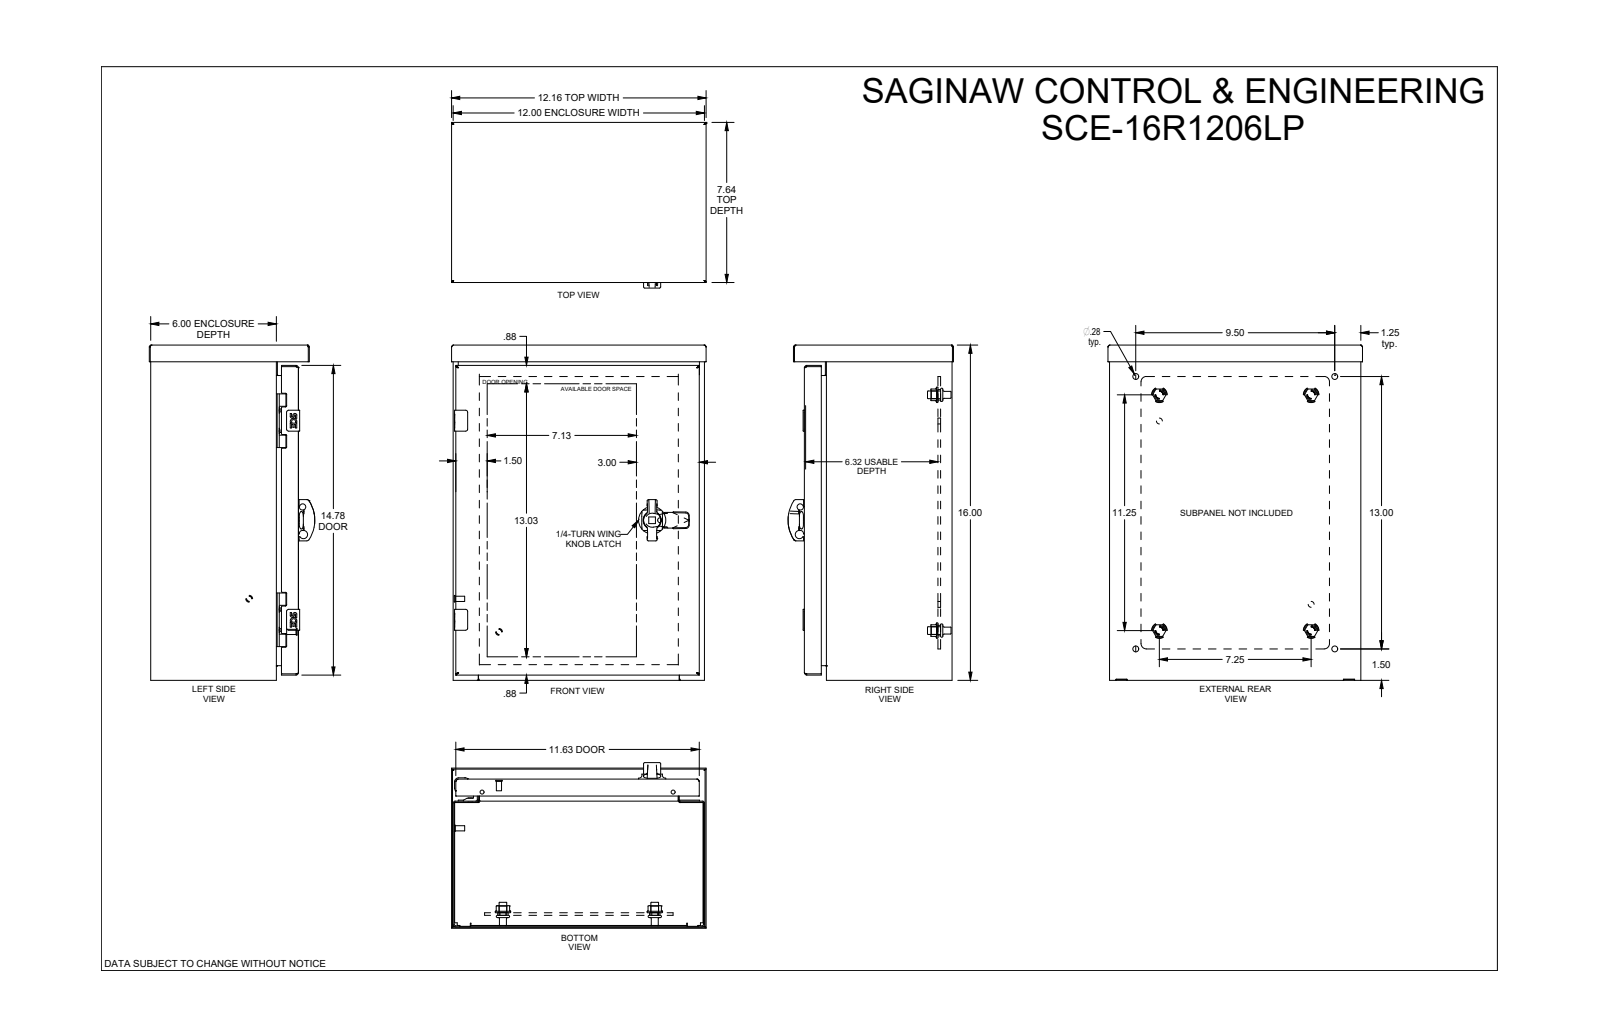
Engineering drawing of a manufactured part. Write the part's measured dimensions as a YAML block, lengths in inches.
part_name: "SCE-16R1206LP_REV2"
step_written_by: "SolidWorks 2021 (AUTOMOTIVE_DESIGN)"
units: inches
bodies: {solids: 25, faces: 1253, planar: 557, cylindrical: 493, other: 203}
overall_size: [16, 12.156, 7.947]
volume: 79.2
surface_area: 2187
round_holes:
  - {diameter: 0.172, count: 4}
  - {diameter: 0.205, count: 4}
  - {diameter: 0.244, count: 4}
  - {diameter: 0.266, count: 4}
  - {diameter: 0.281, count: 4}
  - {diameter: 0.375, count: 4}
  - {diameter: 0.5, count: 4}
  - {diameter: 0.04, count: 2}
  - {diameter: 0.188, count: 2}
  - {diameter: 0.218, count: 2}
  - {diameter: 0.281, count: 2}
  - {diameter: 0.204, count: 1}
round_bosses_or_shafts:
  - {diameter: 0.366, count: 4}
  - {diameter: 0.332, count: 4}
  - {diameter: 0.25, count: 4}
  - {diameter: 0.24, count: 4}
  - {diameter: 0.196, count: 3}
  - {diameter: 0.248, count: 2}
  - {diameter: 1.303, count: 1}
  - {diameter: 0.866, count: 1}
partial_cylinders:
  - {radius: 0.015, count: 36}
  - {radius: 0.06, count: 25}
  - {radius: 0.063, count: 12}
  - {radius: 0.031, count: 10}
  - {radius: 0.062, count: 8}
  - {radius: 0.1, count: 8}
  - {radius: 0.22, count: 8}
  - {radius: 0.03, count: 6}
face_to_face_distances: [0.06, 6.993, 6.933, 11.94, 7.053, 15.94, 0.548, 0.488, 6.445, 6.505]
hole_center_spacings: [9.5, 0.493, 0.494, 0.984, 0.985, 1.25, 1.429, 6]
